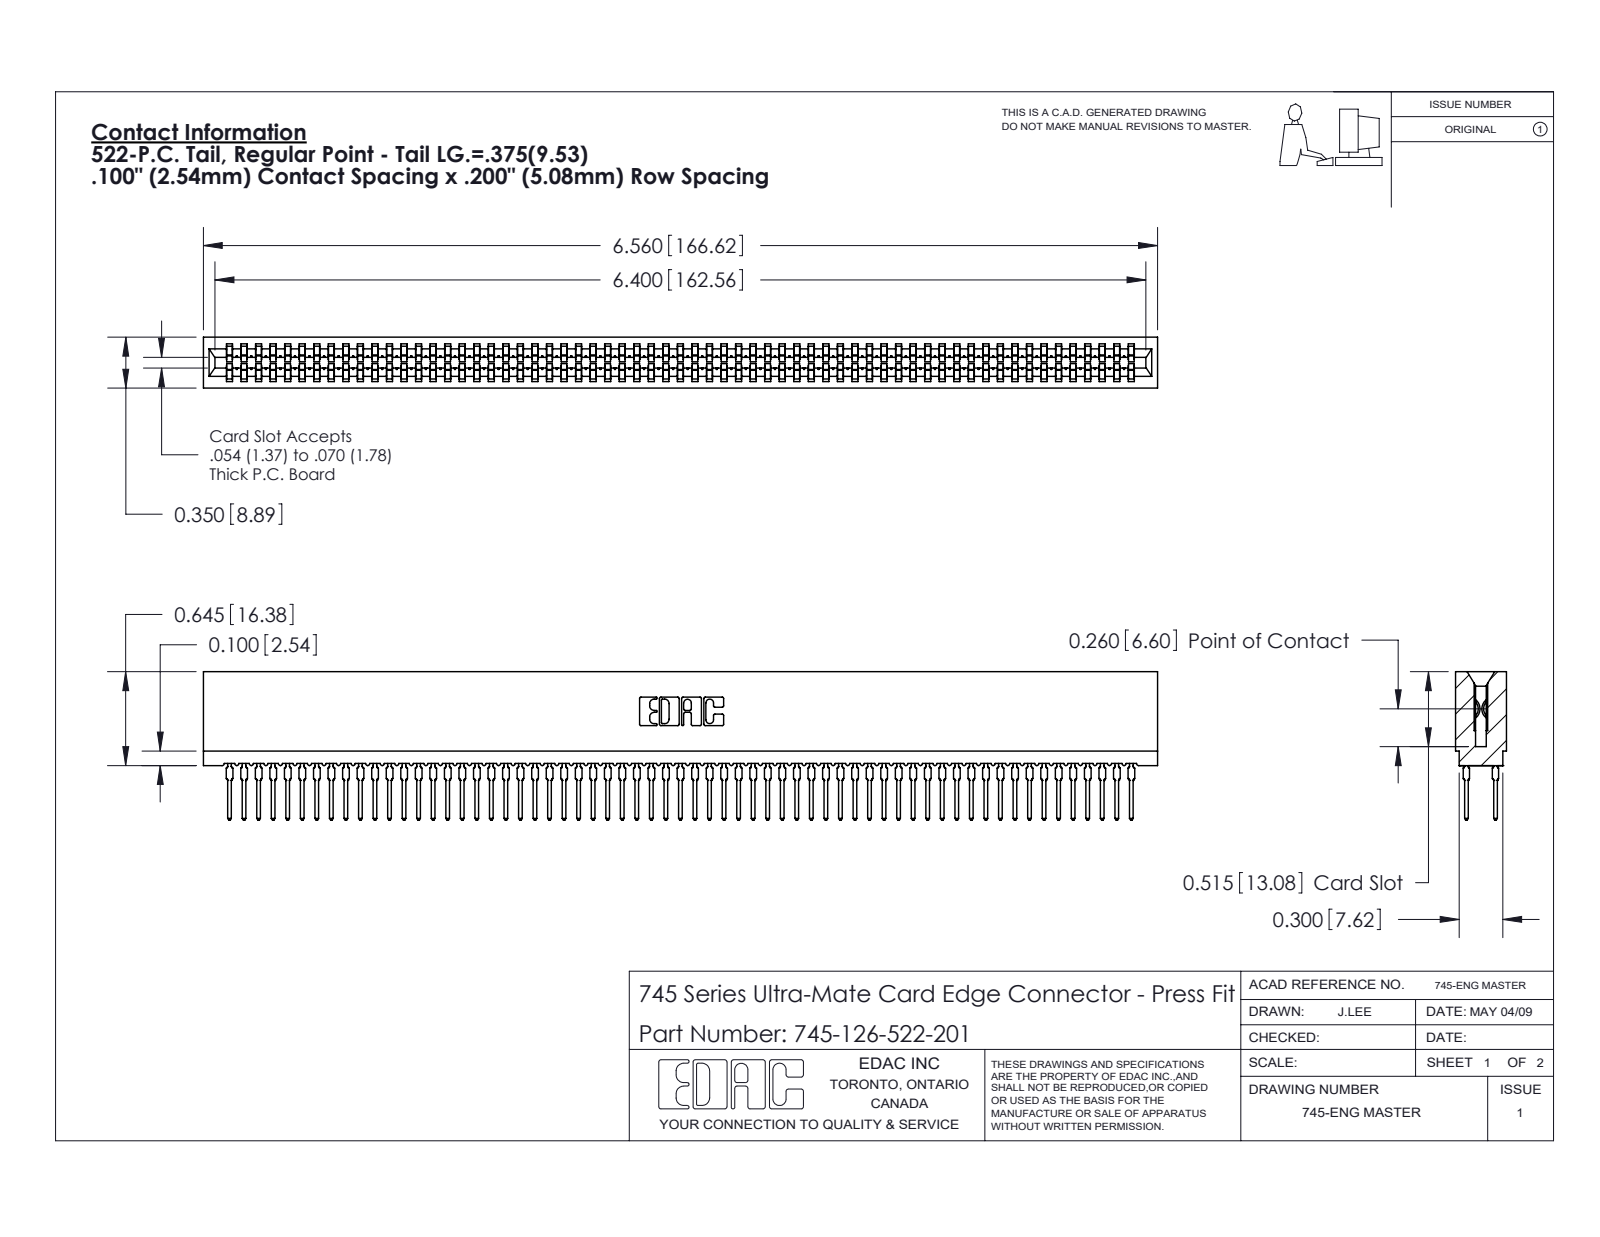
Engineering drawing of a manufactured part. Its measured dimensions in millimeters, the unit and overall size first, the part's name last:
Units: millimetres
Overall size (bounding box): 166.6 × 25.9 × 8.9
Partial cylindrical surfaces — rounded edges, fillets, slot ends (radius × count): R0.5 ×252, R0.4 ×126, R0.3 ×22, R0.1 ×8, R0.3 ×8, R0.2 ×6, R0.8 ×6, R0.7 ×3
Main face-to-face distances: 8.9, 1.6, 7.3, 1.1, 7.7, 0.5, 6.2, 3.5, 5.4, 2.4
Volume: 15 000 mm³ · Surface area: 31 440 mm²
Bodies: 127 solids, 11372 faces (5851 planar, 2245 cylindrical, 3276 other)
Part name (STEP PRODUCT): 745-292-001_522; 745 Part_Insulator Option - 01; 745-126-522-201
STEP written by: SolidWorks 2020 (CONFIG_CONTROL_DESIGN)
